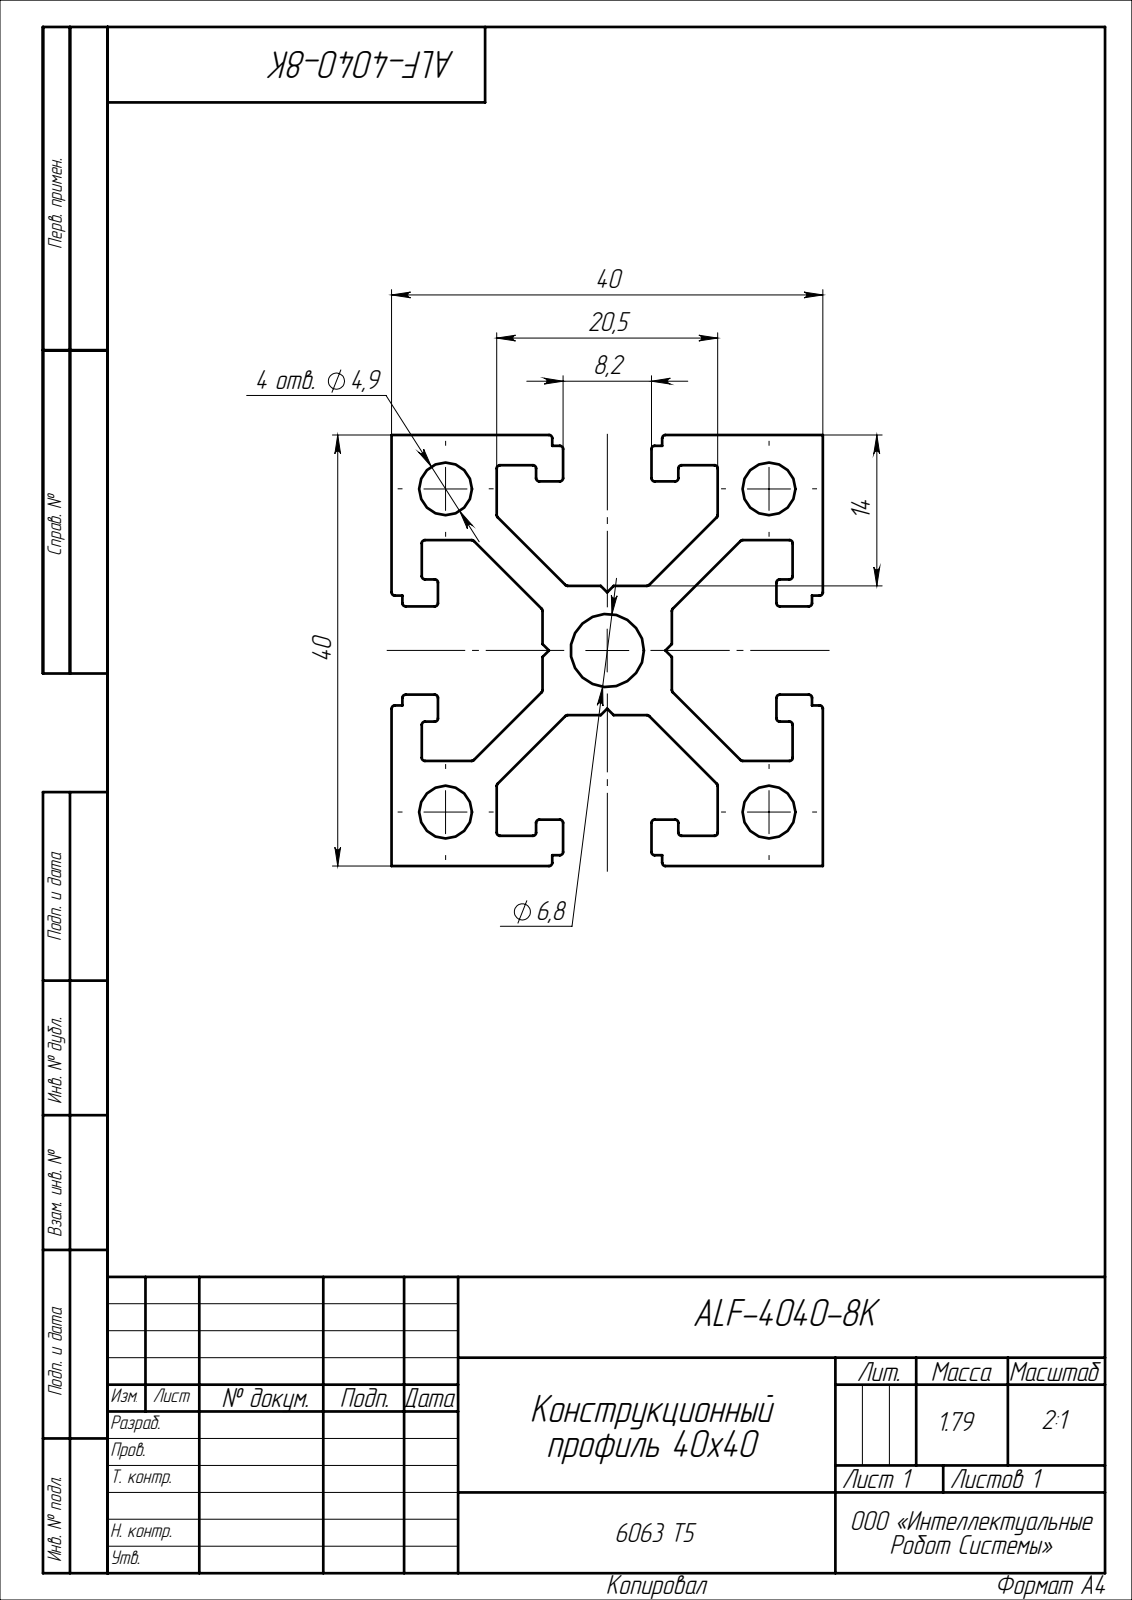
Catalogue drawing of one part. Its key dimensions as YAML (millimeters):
part_name: "ALF-4040-8K"
step_written_by: "SolidWorks 2022 (CONFIG_CONTROL_DESIGN)"
units: millimeters
bodies: {solids: 1, faces: 164, planar: 90, cylindrical: 74, other: 0}
overall_size: [1000, 40, 40]
volume: 664706
surface_area: 444042
round_holes:
  - {diameter: 4.9, count: 4}
  - {diameter: 6.8, count: 1}
partial_cylinders:
  - {radius: 0.3, count: 64}
face_to_face_distances: [40, 3.12, 9.75, 30.25, 24.1, 14, 26, 4.25, 16.25, 2.8]
hole_center_spacings: [21.21, 30, 42.43]
